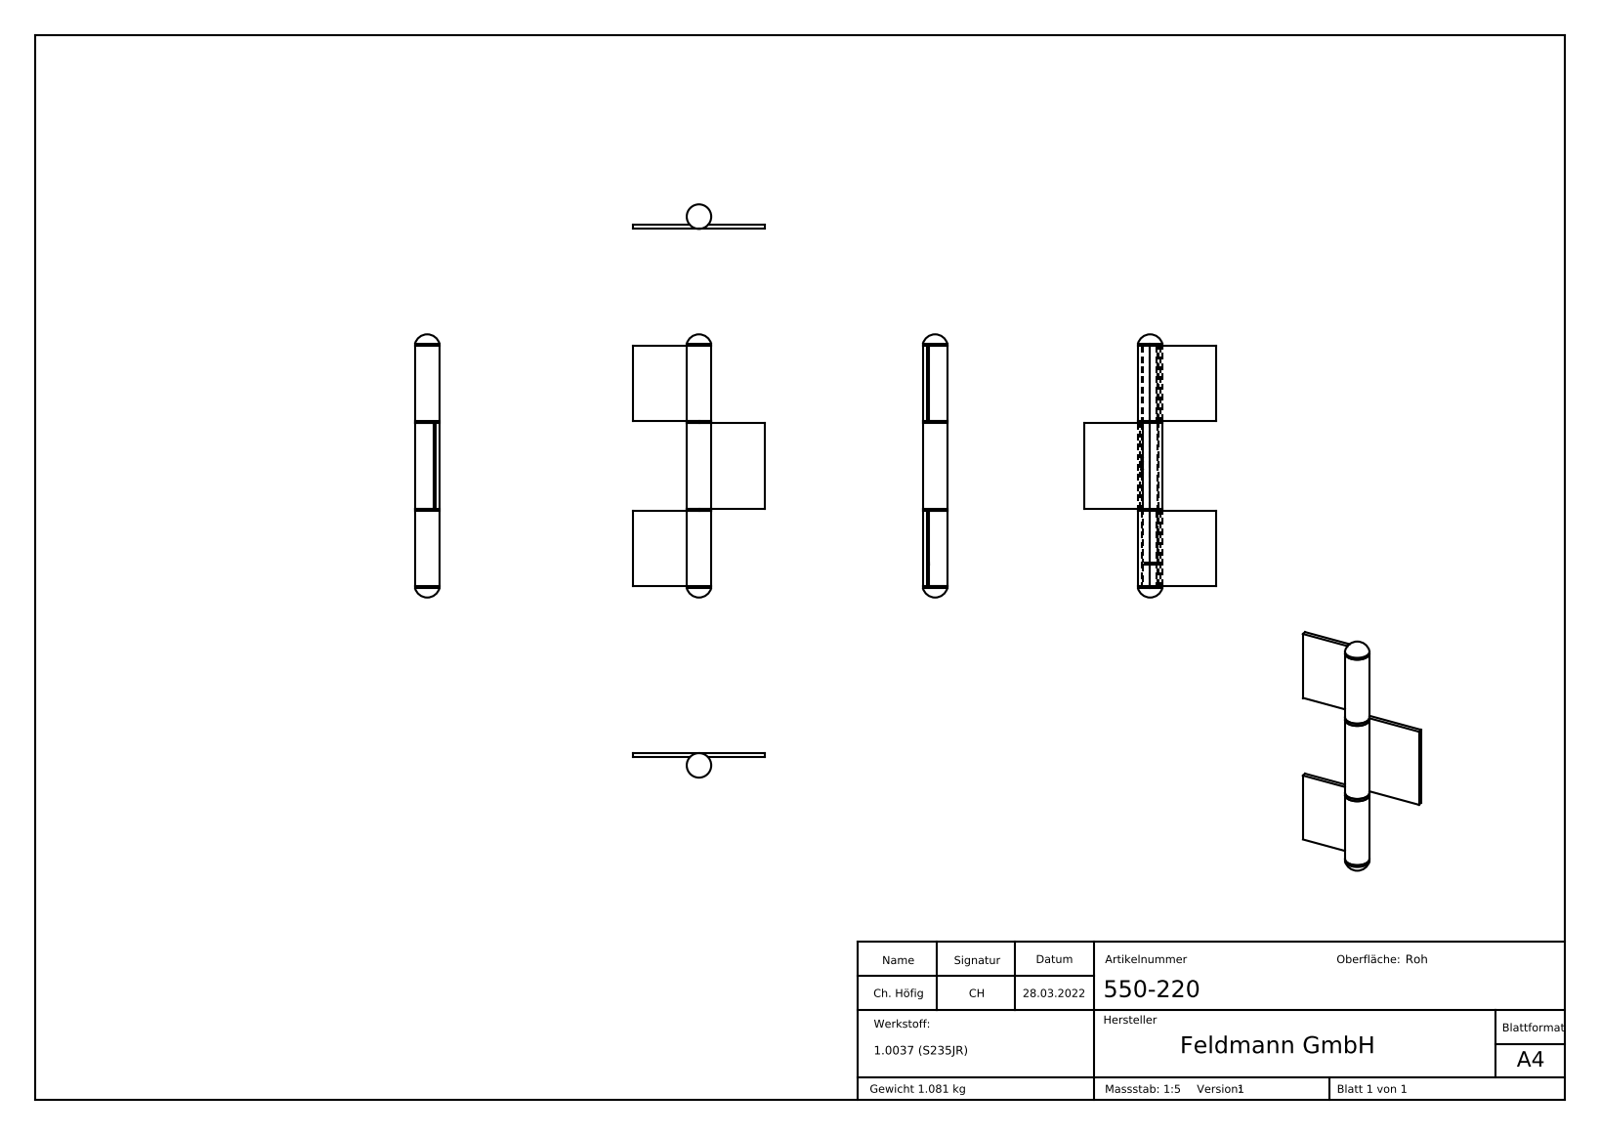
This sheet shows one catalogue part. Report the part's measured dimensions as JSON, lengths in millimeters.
{"part_name": "DIN 125 M4-M20_DIN125 M14; 550-2xx Teil3_550-220 Teil3; 550-220; 550-2xx Teil1_550-220 Teil1 (+2 more)", "step_written_by": "SolidWorks 2018 (CONFIG_CONTROL_DESIGN)", "units": "millimeters", "bodies": {"solids": 7, "faces": 239, "planar": 128, "cylindrical": 14, "other": 97}, "overall_size": [247, 122.99, 23], "volume_mm3": 138563, "surface_area_mm2": 67125, "round_holes": [[15, 1]], "round_bosses_or_shafts": [[23, 1], [13.75, 1]], "face_to_face_distances": [4, 70, 72.5, 152.5, 155, 2.5, 82.5, 225, 85, 80]}
